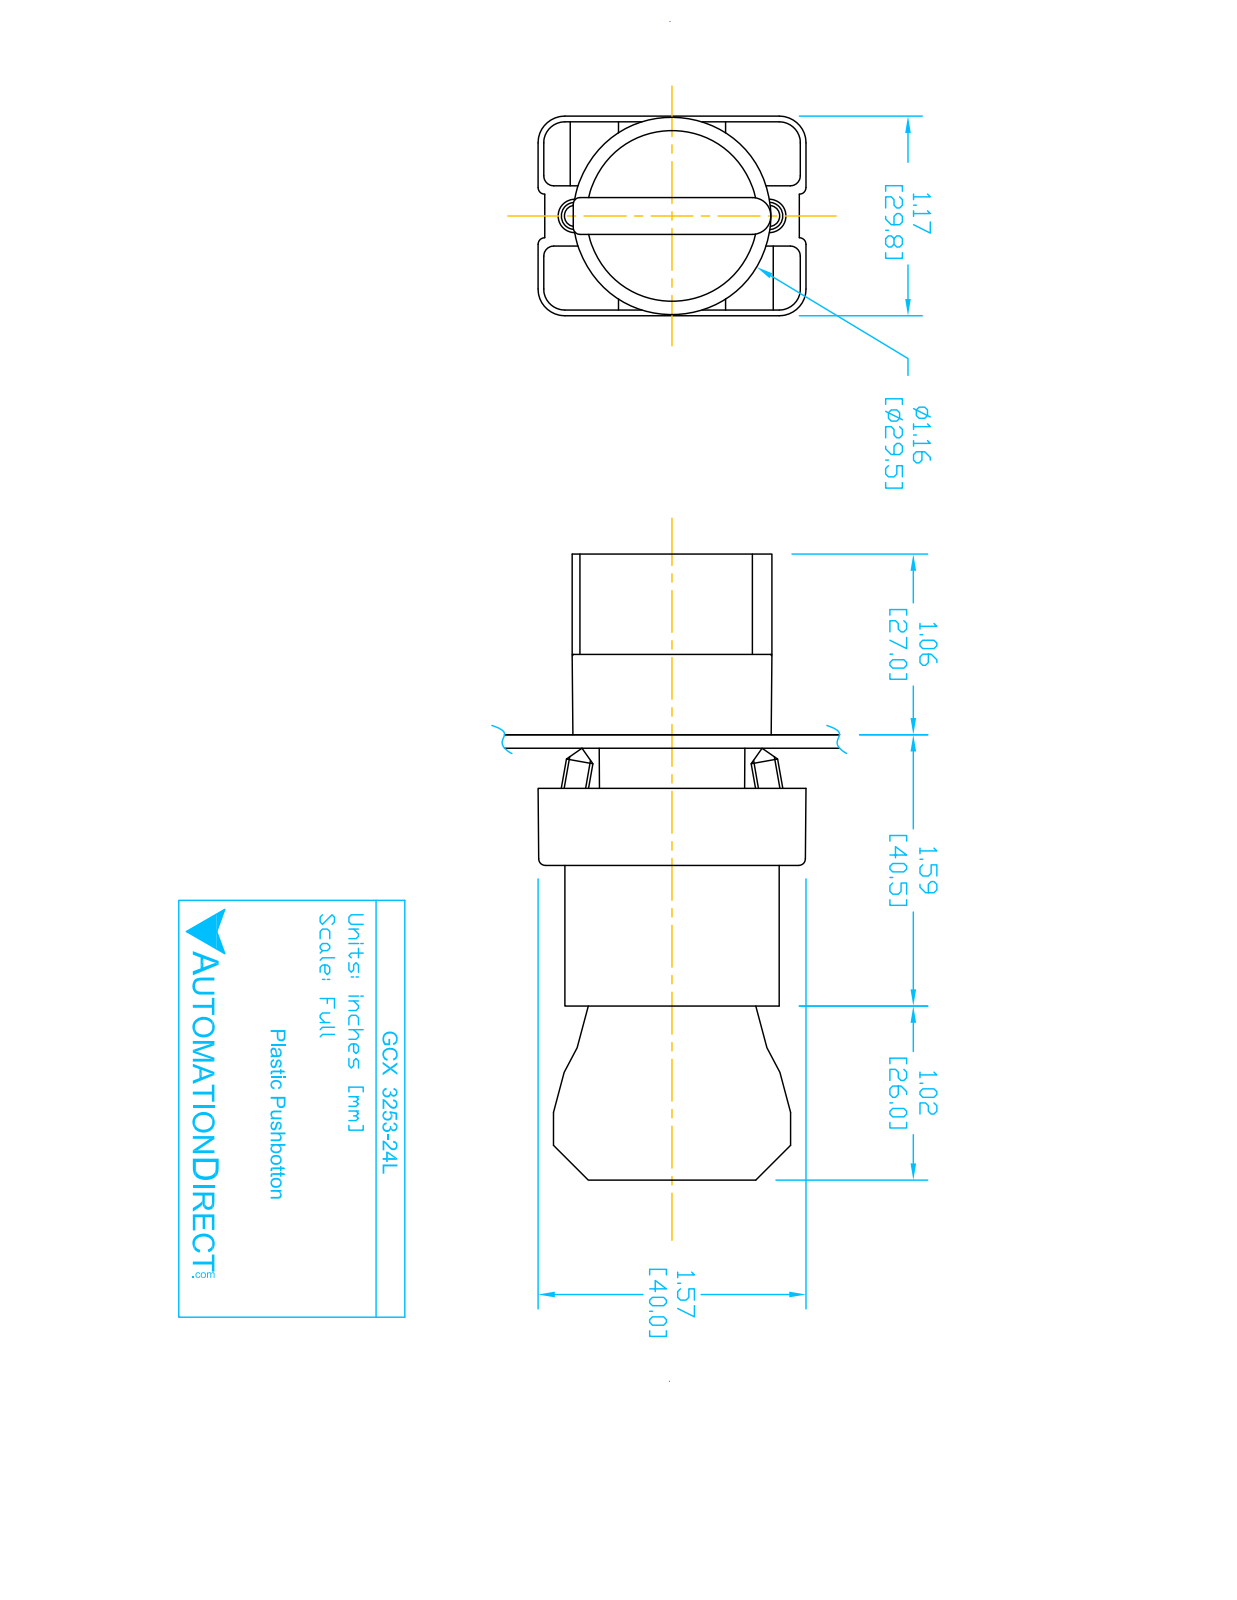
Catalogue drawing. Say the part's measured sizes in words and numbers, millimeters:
The part is named "ecx1040; GCX3253L OPERATOR; ECX1050; ECX3029-2 (+1 more)". Its 3-D file was written by "SolidWorks 2016 (AUTOMOTIVE_DESIGN)". It is 8 solids with 445 faces: 263 planar, 151 cylindrical and 31 other. Overall it measures 92.8 by 40.2 by 29.9 millimeters. Its volume is 45 870 cubic millimeters and its surface area 25 160 square millimeters. Round holes: 2 of diameter 2, 2 of diameter 3.1, 2 of diameter 3.3, 1 of diameter 2.2, 1 of diameter 5, 1 of diameter 11.9, 1 of diameter 22.3, 1 of diameter 22.6, 1 of diameter 26. Round bosses or shafts: 4 of diameter 4, 1 of diameter 29.8, 1 of diameter 25.5, 1 of diameter 24, 1 of diameter 21.7, 1 of diameter 19.8, 1 of diameter 12.8. Partial cylindrical surfaces (rounded edges, fillets, slot ends): 24 of radius 1.5, 12 of radius 1, 12 of radius 3.1, 12 of radius 4, 9 of radius 1, 2 of radius 3.3, 1 of radius 0.5, 1 of radius 1.6. The main face-to-face distances are 21, 51.3, 30.3, 14.7, 31.6, 29.7, 12, 11.9, 0.8, 0.8. The hole center spacings are 6, 13.8, 12, 12.4.
